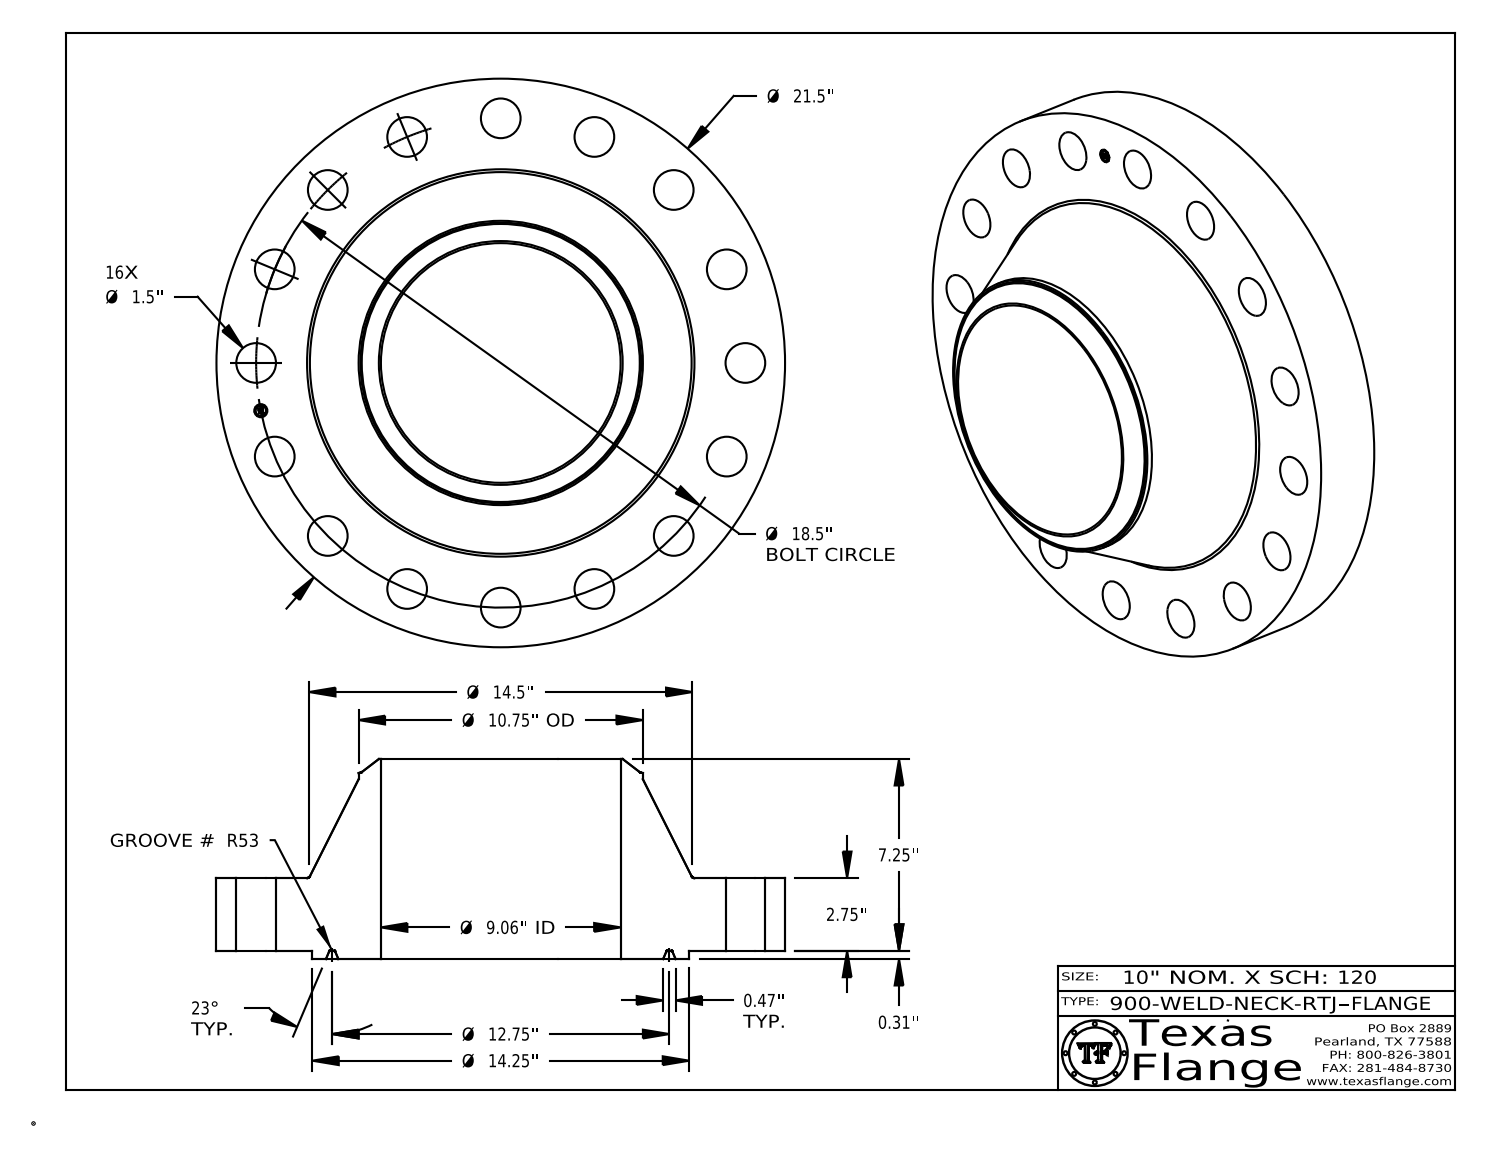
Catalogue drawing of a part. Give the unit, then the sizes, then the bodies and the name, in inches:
Units: inches
Overall size (bounding box): 21.5 × 21.5 × 7.563
Round holes (diameter × count): ⌀1.5 ×16, ⌀0.495 ×1, ⌀9.062 ×1
Round bosses / shafts (diameter × count): ⌀0.03 ×8, ⌀21.5 ×1, ⌀14.25 ×1, ⌀10.75 ×1, ⌀0.39 ×1
Main face-to-face distances: 2.75, 0.313, 3.063, 7.563, 7.25, 4.5, 3.048, 2.735, 0.015, 4.515
Hole centre spacings: 15.382, 7.08, 9.25, 13.081, 3.609, 3.609, 10.278, 10.278
Volume: 1 012 in³ · Surface area: 1 283 in²
Bodies: 1 solid, 449 faces (371 planar, 60 cylindrical, 18 other)
Part name (STEP PRODUCT): 900-WELD-NECK-RTJ
STEP written by: CATIA V5 STEP AP214 (AUTOMOTIVE_DESIGN)
